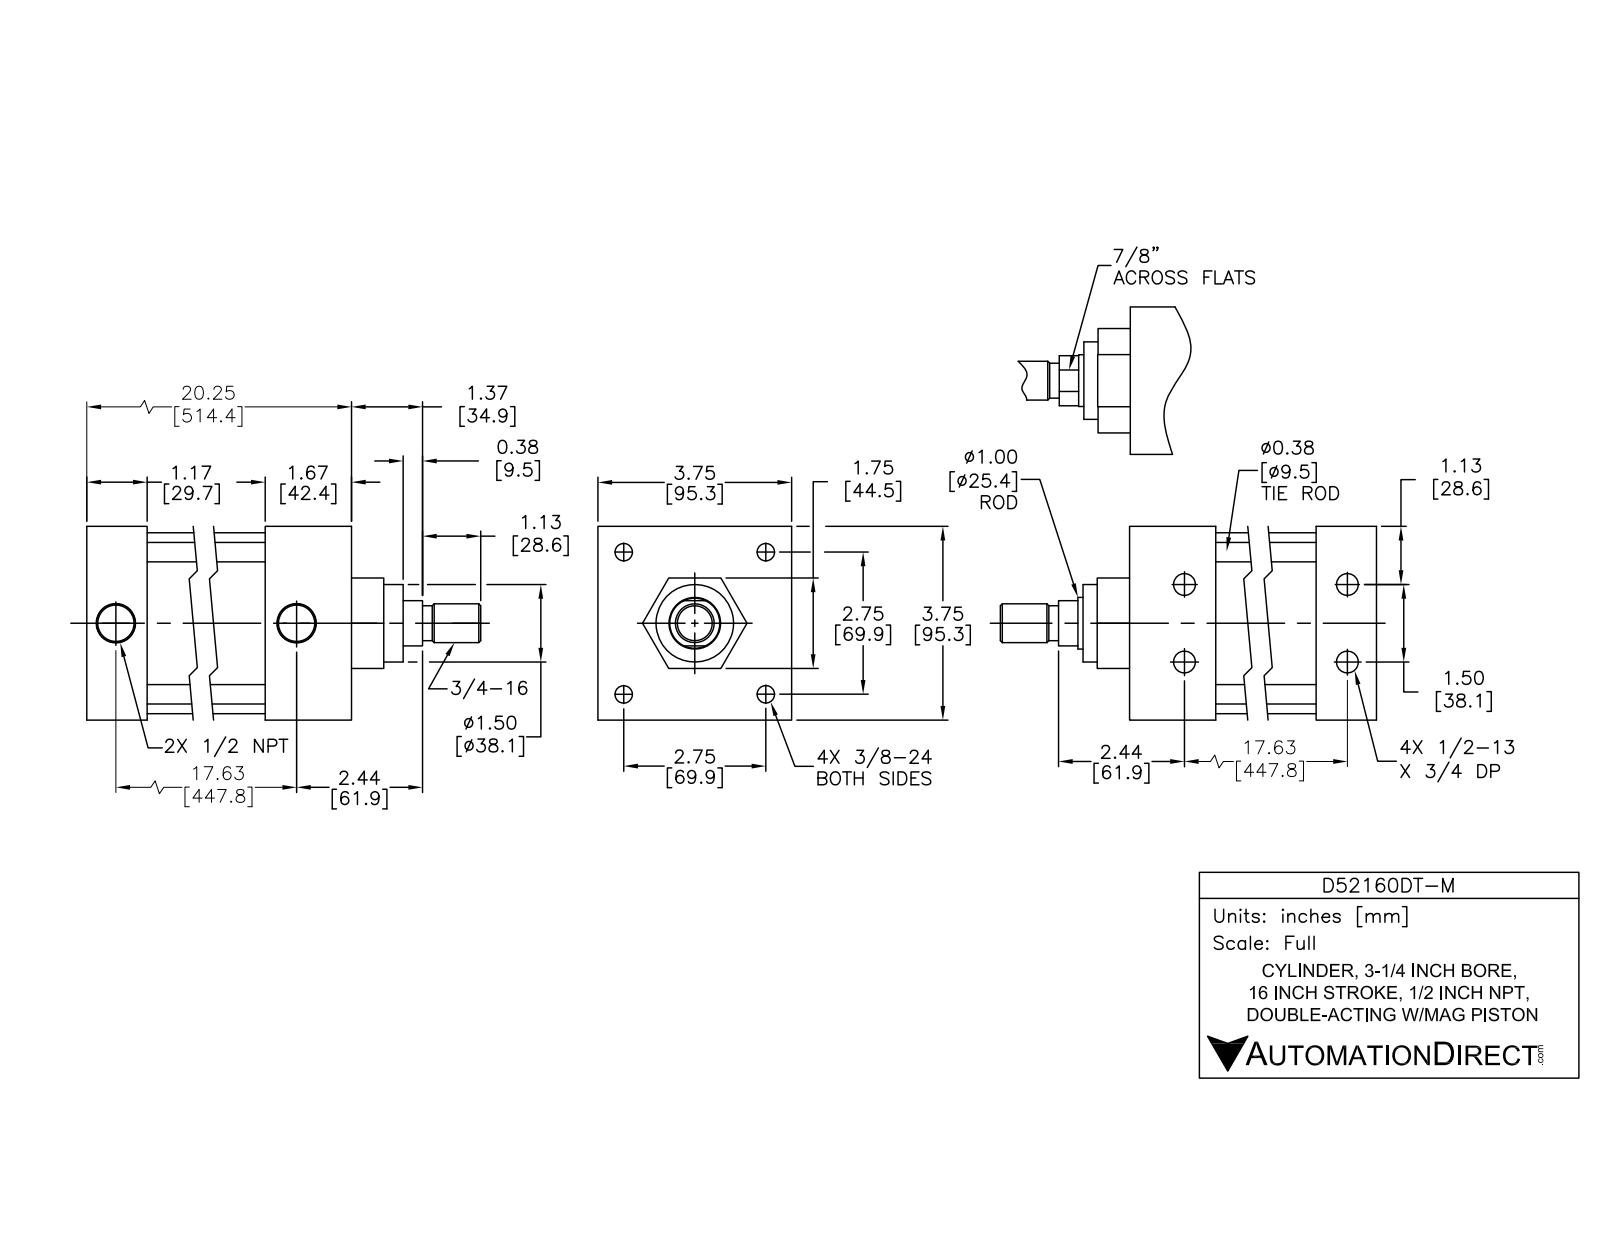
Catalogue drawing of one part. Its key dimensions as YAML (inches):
part_name: "D52160DT-M; D52160DT-M PISTON; D52160DT-M BODY"
step_written_by: "SolidWorks 2015 (AUTOMOTIVE_DESIGN)"
units: inches
bodies: {solids: 12, faces: 303, planar: 99, cylindrical: 114, other: 90}
overall_size: [22.745, 3.75, 3.75]
volume: 93.34
surface_area: 694.8
round_holes:
  - {diameter: 0.33, count: 4}
  - {diameter: 0.406, count: 4}
  - {diameter: 0.417, count: 4}
  - {diameter: 0.625, count: 4}
  - {diameter: 0.5, count: 2}
  - {diameter: 0.766, count: 2}
  - {diameter: 1, count: 1}
  - {diameter: 1.003, count: 1}
  - {diameter: 3.25, count: 1}
round_bosses_or_shafts:
  - {diameter: 0.609, count: 4}
  - {diameter: 0.375, count: 4}
  - {diameter: 0.34, count: 4}
  - {diameter: 3.5, count: 1}
  - {diameter: 3.247, count: 1}
  - {diameter: 1.75, count: 1}
  - {diameter: 0.997, count: 1}
  - {diameter: 0.97, count: 1}
partial_cylinders:
  - {radius: 0.375, count: 4}
face_to_face_distances: [3.75, 0.08, 17.326, 20.246, 1.75, 18.997, 1.249, 17.751, 1.246, 2.495]
hole_center_spacings: [0.75, 0.76, 1.5, 1.95, 1.95, 2.758, 2.758, 3.9]
